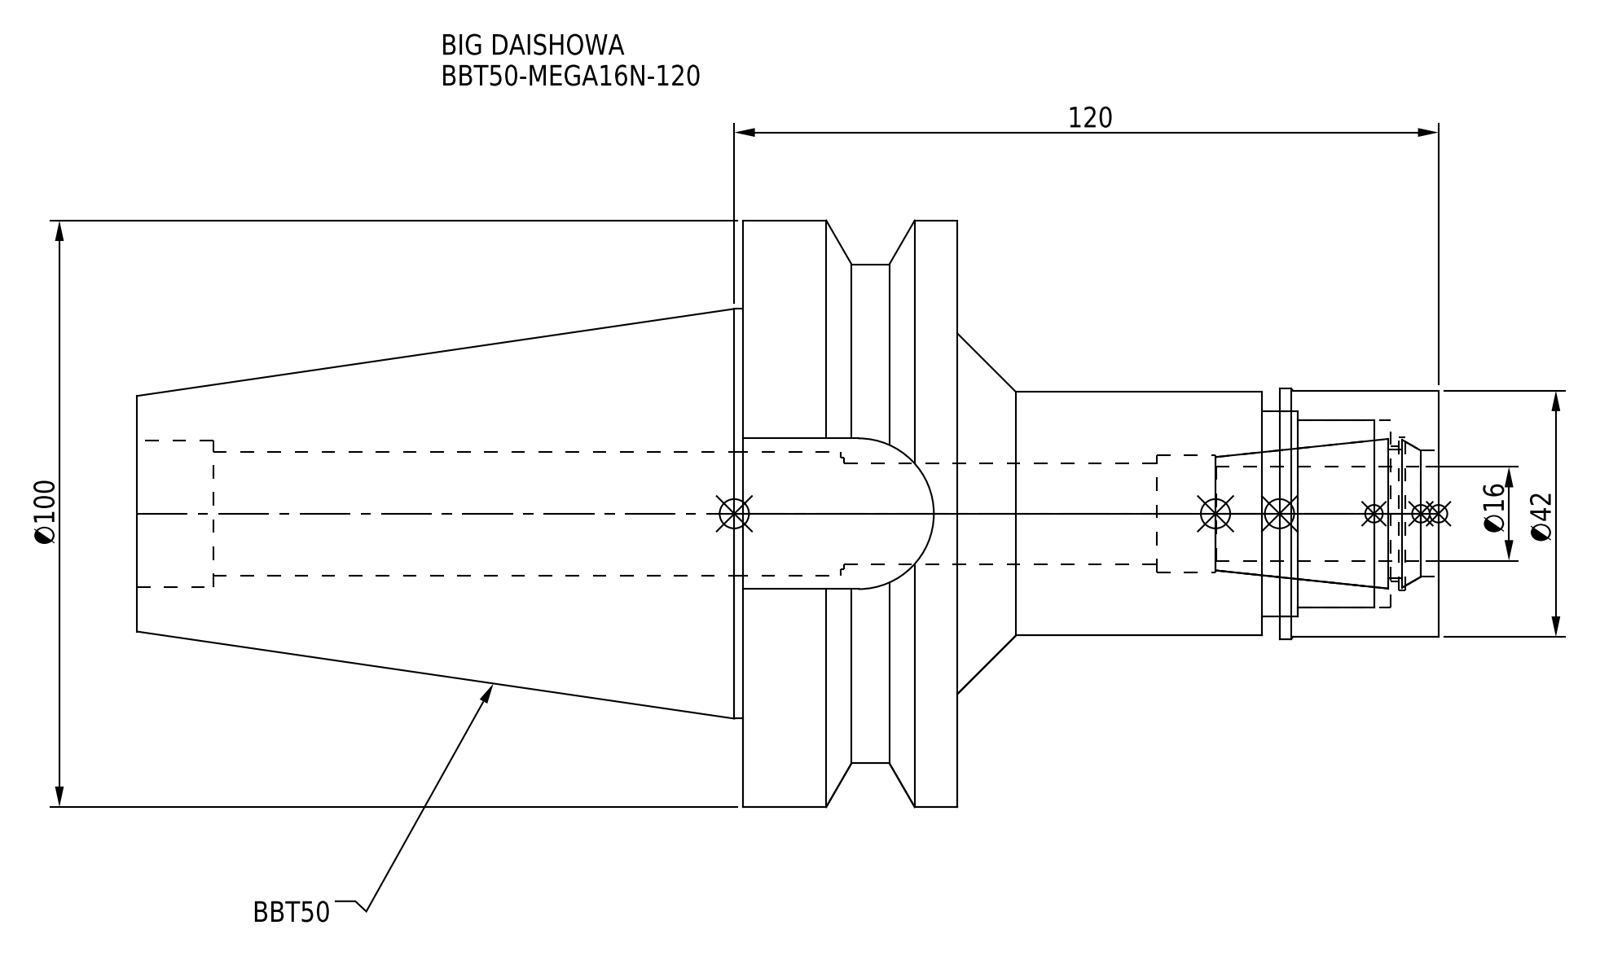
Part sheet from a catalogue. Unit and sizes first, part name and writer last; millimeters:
Units: millimetres
Overall size (bounding box): 221.8 × 100 × 100
Round holes (diameter × count): ⌀17.3 ×1, ⌀19 ×1, ⌀20 ×1, ⌀21.2 ×1, ⌀21.5 ×1, ⌀23 ×1, ⌀25 ×1, ⌀26 ×1, ⌀32 ×1, ⌀35 ×1
Round bosses / shafts (diameter × count): ⌀100 ×1, ⌀85 ×1, ⌀69.85 ×1, ⌀42.7 ×1, ⌀42 ×1, ⌀41.5 ×1
Partial cylindrical surfaces — rounded edges, fillets, slot ends (radius × count): R12.85 ×1
Main face-to-face distances: 36.5, 82, 118.5, 221.8, 139.8, 103.3, 70.8, 27.1, 54.9, 91.4
Volume: 541 204 mm³ · Surface area: 74 794 mm²
Bodies: 2 solids, 79 faces (23 planar, 42 cylindrical, 14 other)
Part name (STEP PRODUCT): DXF_TEMP_ASSY_ASM_4_ASM.stp; BBT50MN16120-160_ASM.stp; BBT50-MEGA16N-120-160-FreeParts; BBT50-MEGA16N-120_1.stp (+3 more)
STEP written by: SolidWorks 2019 (CONFIG_CONTROL_DESIGN)
